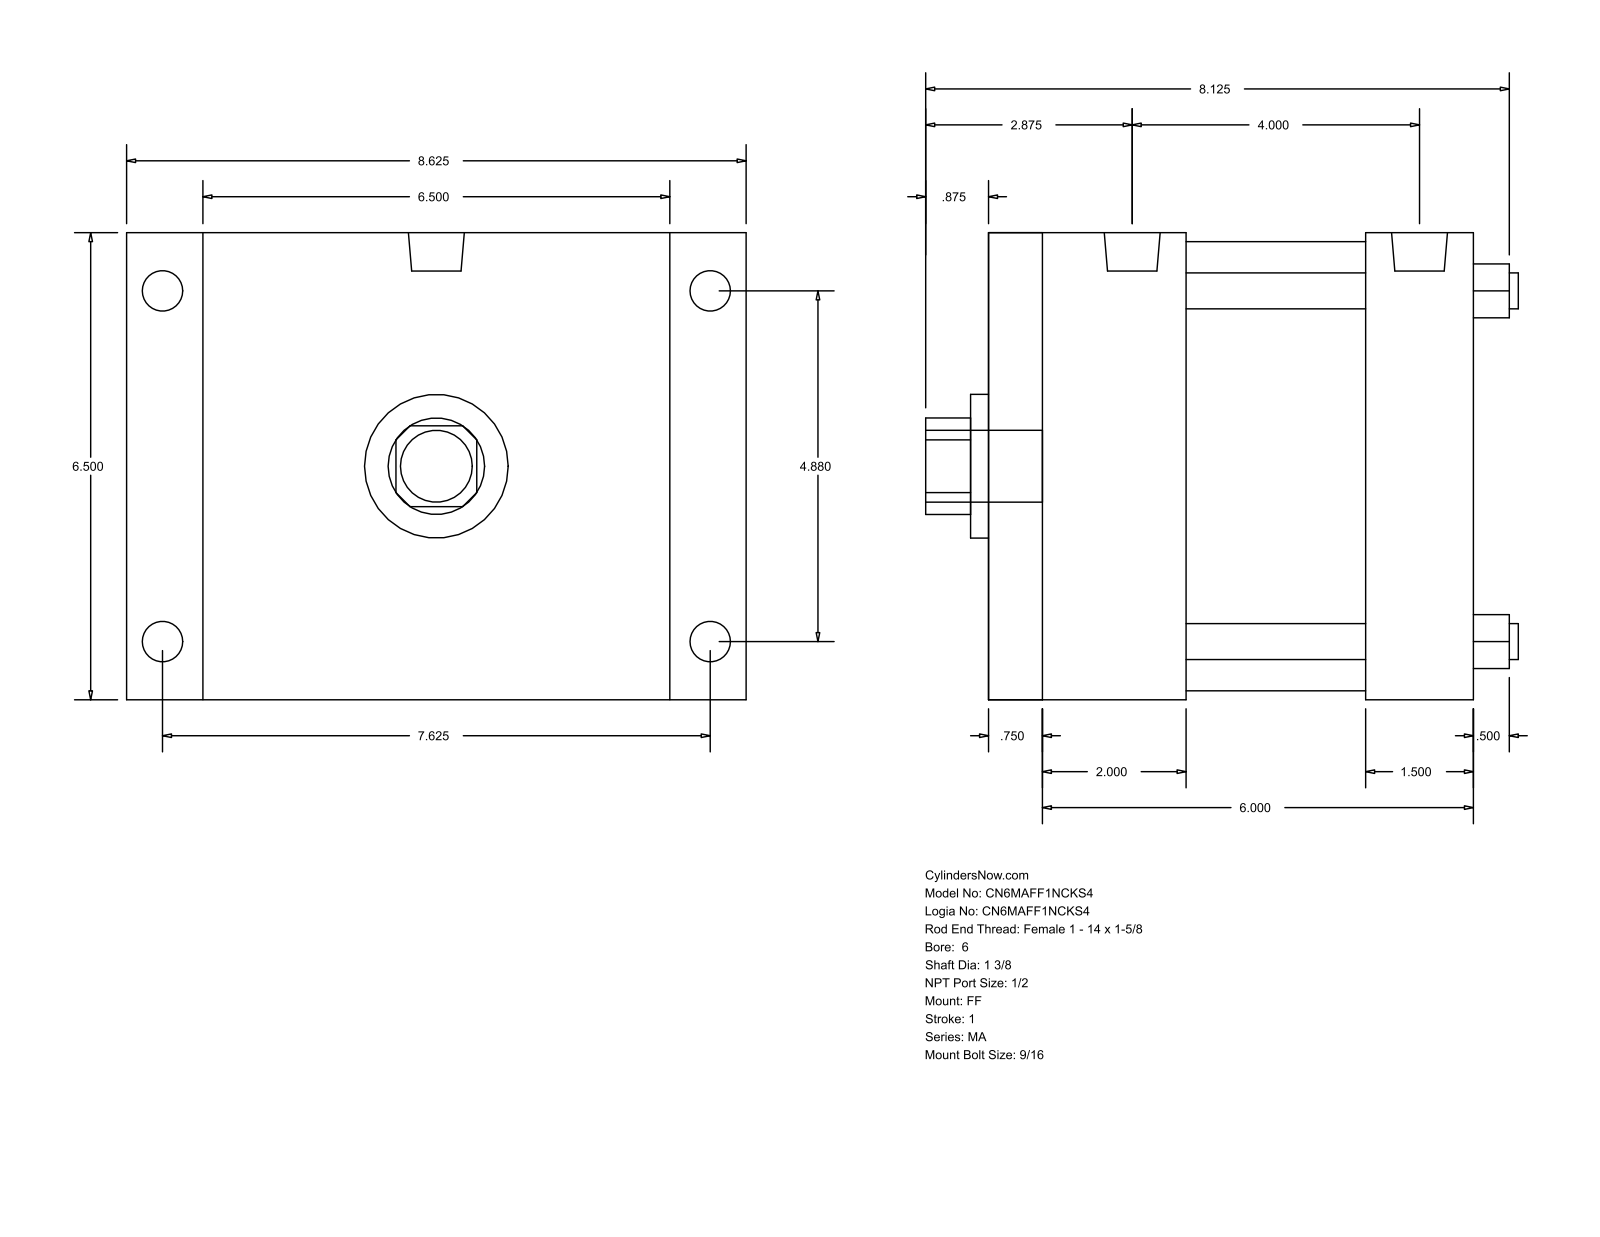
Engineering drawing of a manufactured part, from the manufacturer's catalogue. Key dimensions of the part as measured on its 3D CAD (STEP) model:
Part name (STEP PRODUCT): MA_FF__0600_1.375
STEP written by: GSSL Pune (CONFIG_CONTROL_DESIGN)
Units: millimetres
Bodies: 0 solids, 92 faces (64 planar, 28 cylindrical, 0 other)
Overall size (bounding box): 219.07 × 209.55 × 165.1
Round holes (diameter × count): ⌀12.7 ×4, ⌀34.92 ×1, ⌀50.8 ×1, ⌀158.75 ×1
Round bosses / shafts (diameter × count): ⌀17.46 ×4, ⌀14.29 ×4, ⌀19.77 ×2, ⌀25.4 ×1
Partial cylindrical surfaces — rounded edges, fillets, slot ends (radius × count): R17.06 ×1
Main face-to-face distances: 165.1, 171.45, 66.67, 15.87, 155.58, 50.8, 104.78, 133.34, 117.47, 38.11
Hole centre spacings: 87.65, 123.96, 175.31
